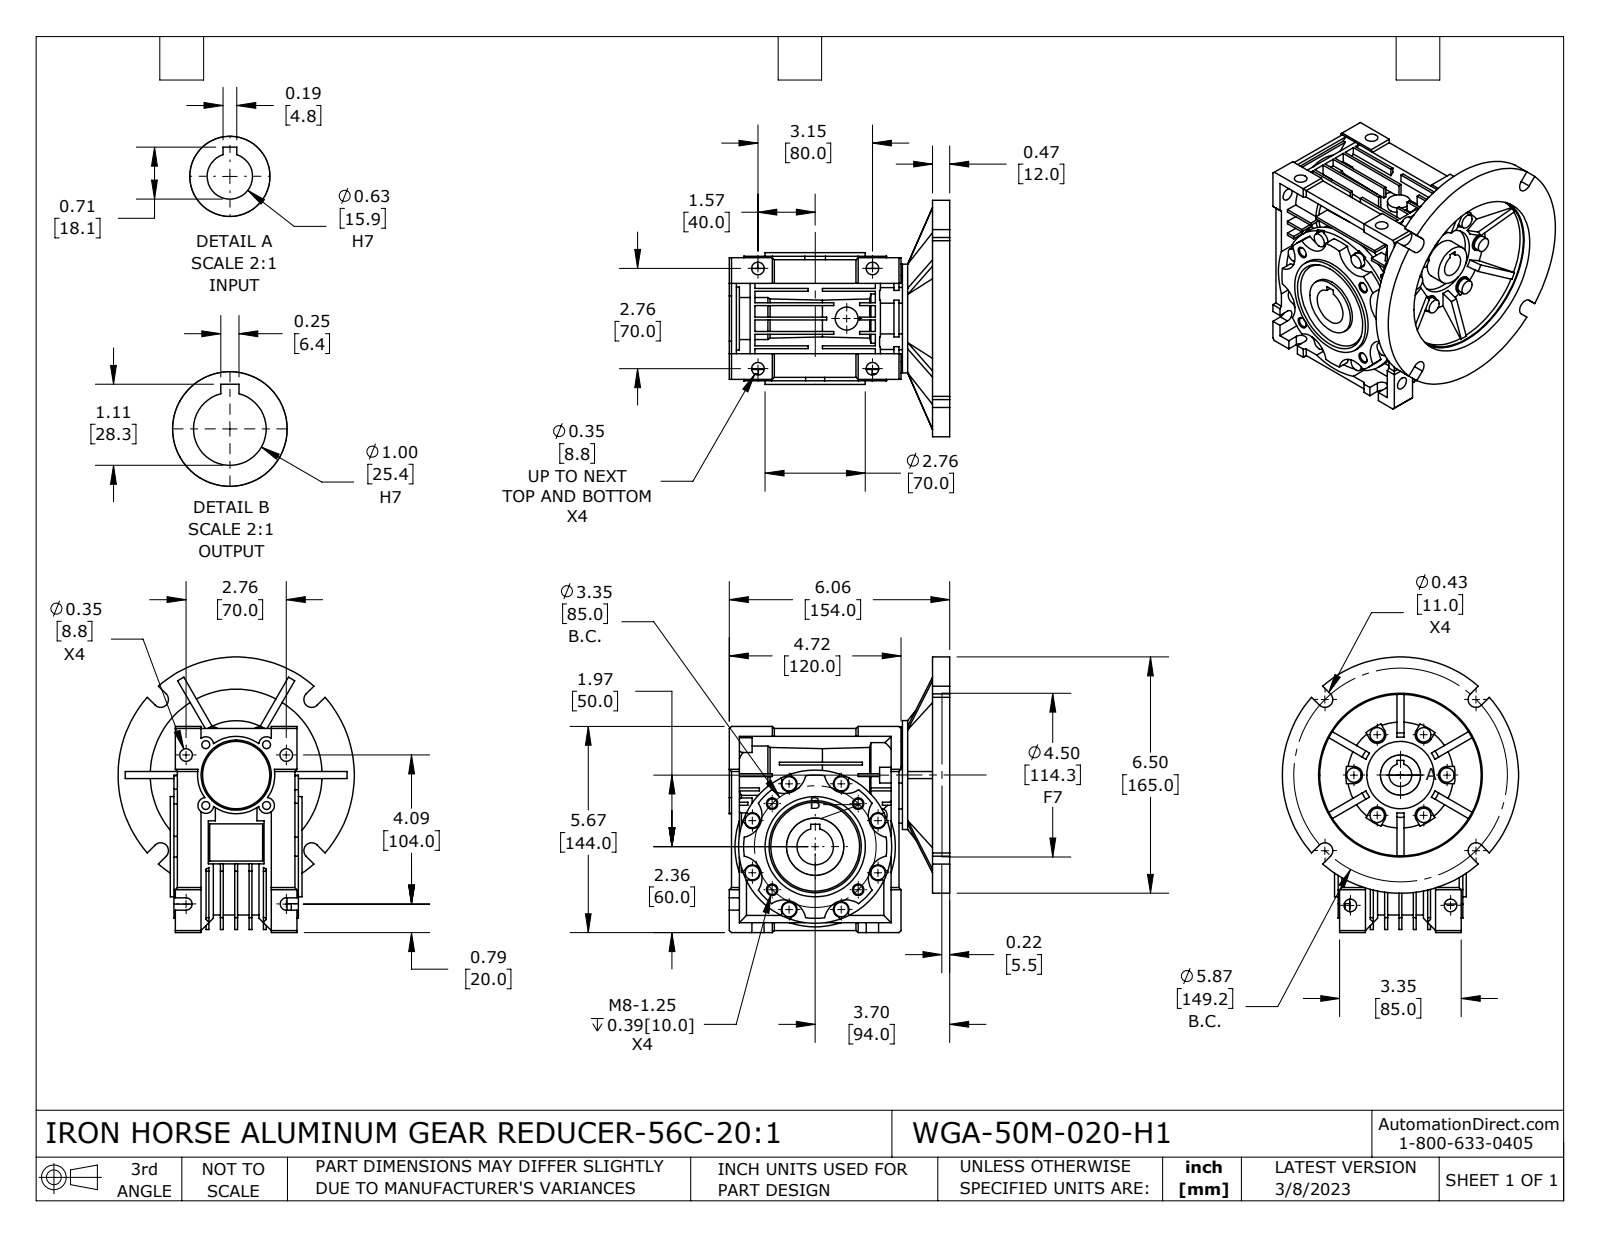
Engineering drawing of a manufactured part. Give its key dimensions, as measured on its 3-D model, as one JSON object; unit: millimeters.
{"part_name": "WGA-50M-020-H1", "step_written_by": "SolidWorks 2021 (CONFIG_CONTROL_DESIGN)", "units": "millimeters", "bodies": {"solids": 4, "faces": 954, "planar": 558, "cylindrical": 292, "other": 104}, "overall_size": [192.5, 165, 154], "volume_mm3": 1191000, "surface_area_mm2": 266100, "round_holes": [[8.8, 8], [5.6, 4], [6.7, 4], [6.7, 2], [15.9, 1], [16.5, 1], [25.4, 1], [28, 1], [34, 1], [40, 1], [47, 1], [112.8, 1]], "round_bosses_or_shafts": [[10, 14], [165, 1], [107, 1], [76, 1], [70, 1], [61, 1], [55, 1], [54, 1]], "partial_cylinders_radius": [[5.5, 22], [6, 14], [15, 8], [15.5, 8], [4.2, 6], [46, 1], [47.7, 1], [50, 1]], "face_to_face_distances": [12, 10, 2, 7, 8, 1.5, 5.5, 20, 55, 35], "hole_center_spacings": [30, 42.4, 42.5, 60.1, 70, 15.6, 37.7, 37.8]}
